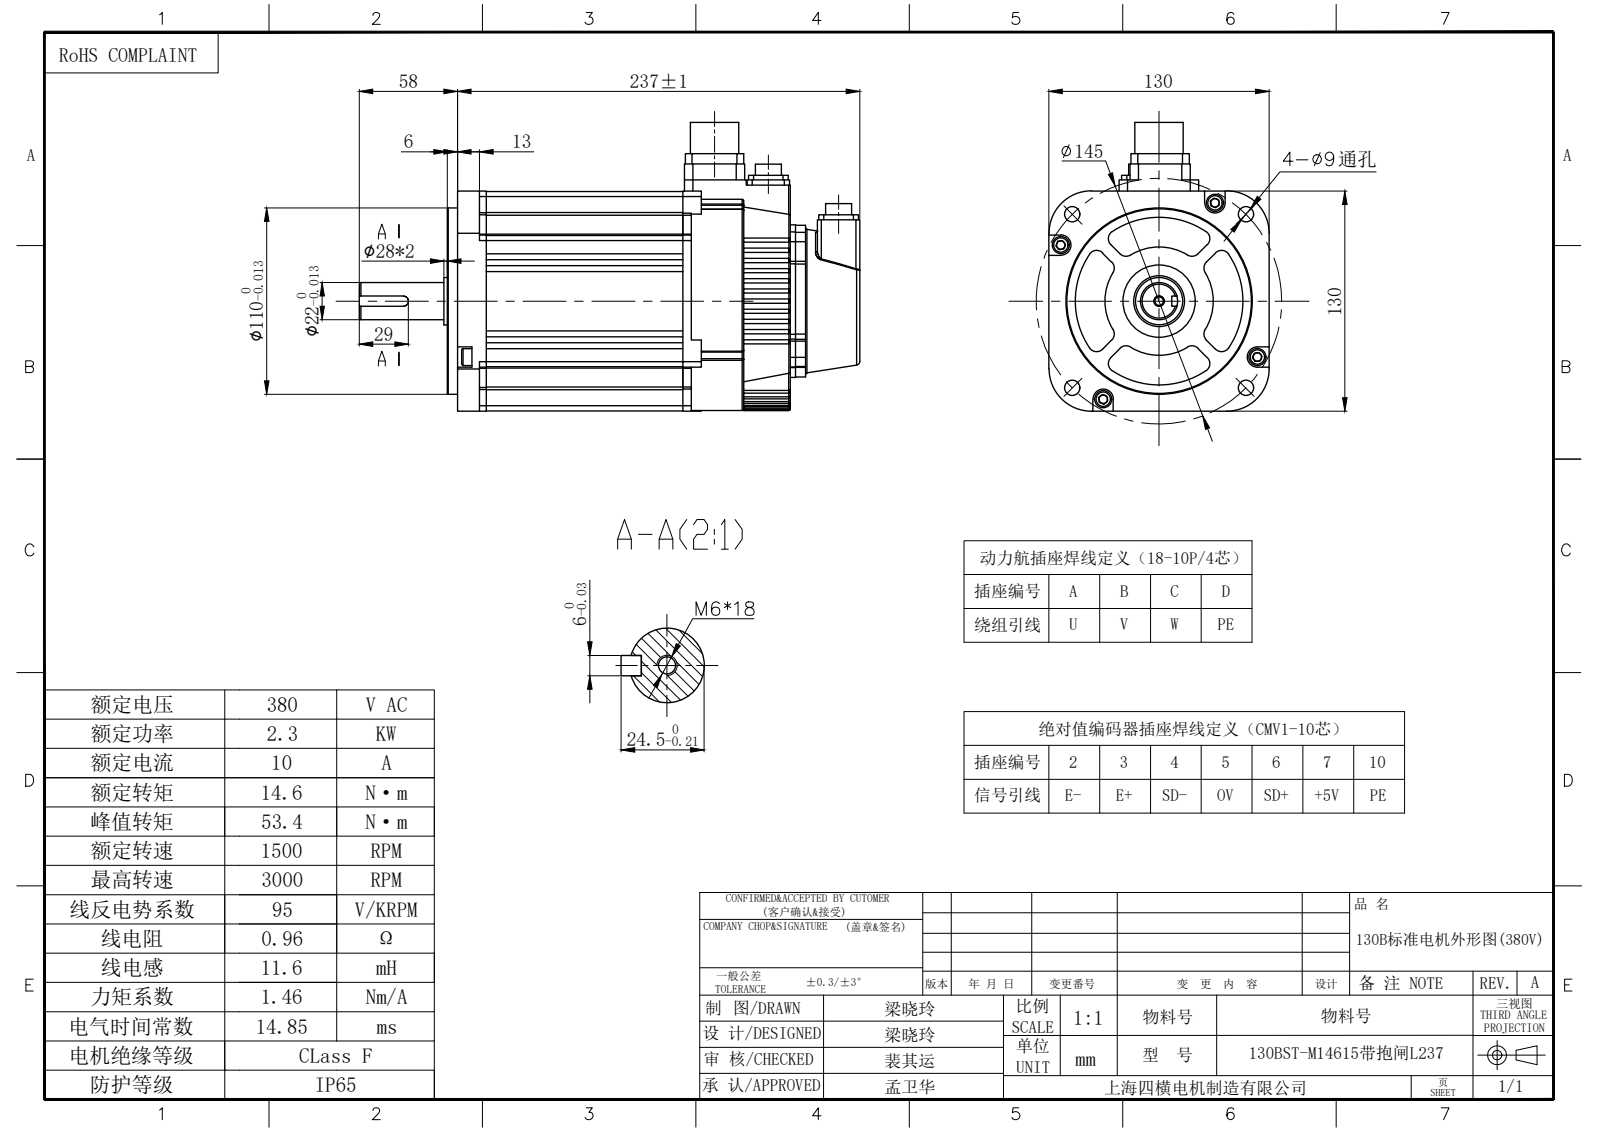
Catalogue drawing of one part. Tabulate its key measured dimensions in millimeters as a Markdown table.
| quantity | value |
| --- | --- |
| part name | 130BST机身116; 130BST后盖; hexagon socket head cap screws gb_ M6; 130BST前端盖出轴 (+2 more) |
| STEP written by | SolidWorks 2020 (AUTOMOTIVE_DESIGN) |
| units | millimeters |
| bodies | 8 solids, 1030 faces (411 planar, 412 cylindrical, 207 other) |
| overall size | 295.5 × 170.5 × 130 |
| volume | 3 033 000 mm³ |
| surface area | 253 973 mm² |
| round holes (diameter × count) | 3 × 14, 6.6 × 8, 5 × 5, 9 × 4, 11.5 × 2, 24 × 1, 42.6 × 1 |
| round bosses / shafts (diameter × count) | 10 × 4, 6 × 4, 2.5 × 4, 15.3 × 2, 2 × 2, 129 × 1, 110 × 1, 30 × 1 |
| partial cylindrical surfaces (radius × count) | 1 × 61, 3 × 25, 5 × 22, 1.5 × 16, 3.25 × 16, 2 × 8, 3.5 × 8, 2.25 × 4 |
| main face-to-face distances | 116, 179.5, 63.5, 133, 129.5, 17, 196.5, 26, 103.5, 3.5 |
| hole center spacings | 18, 1.34, 12.02, 12.73, 17, 27, 66.73, 68 |
